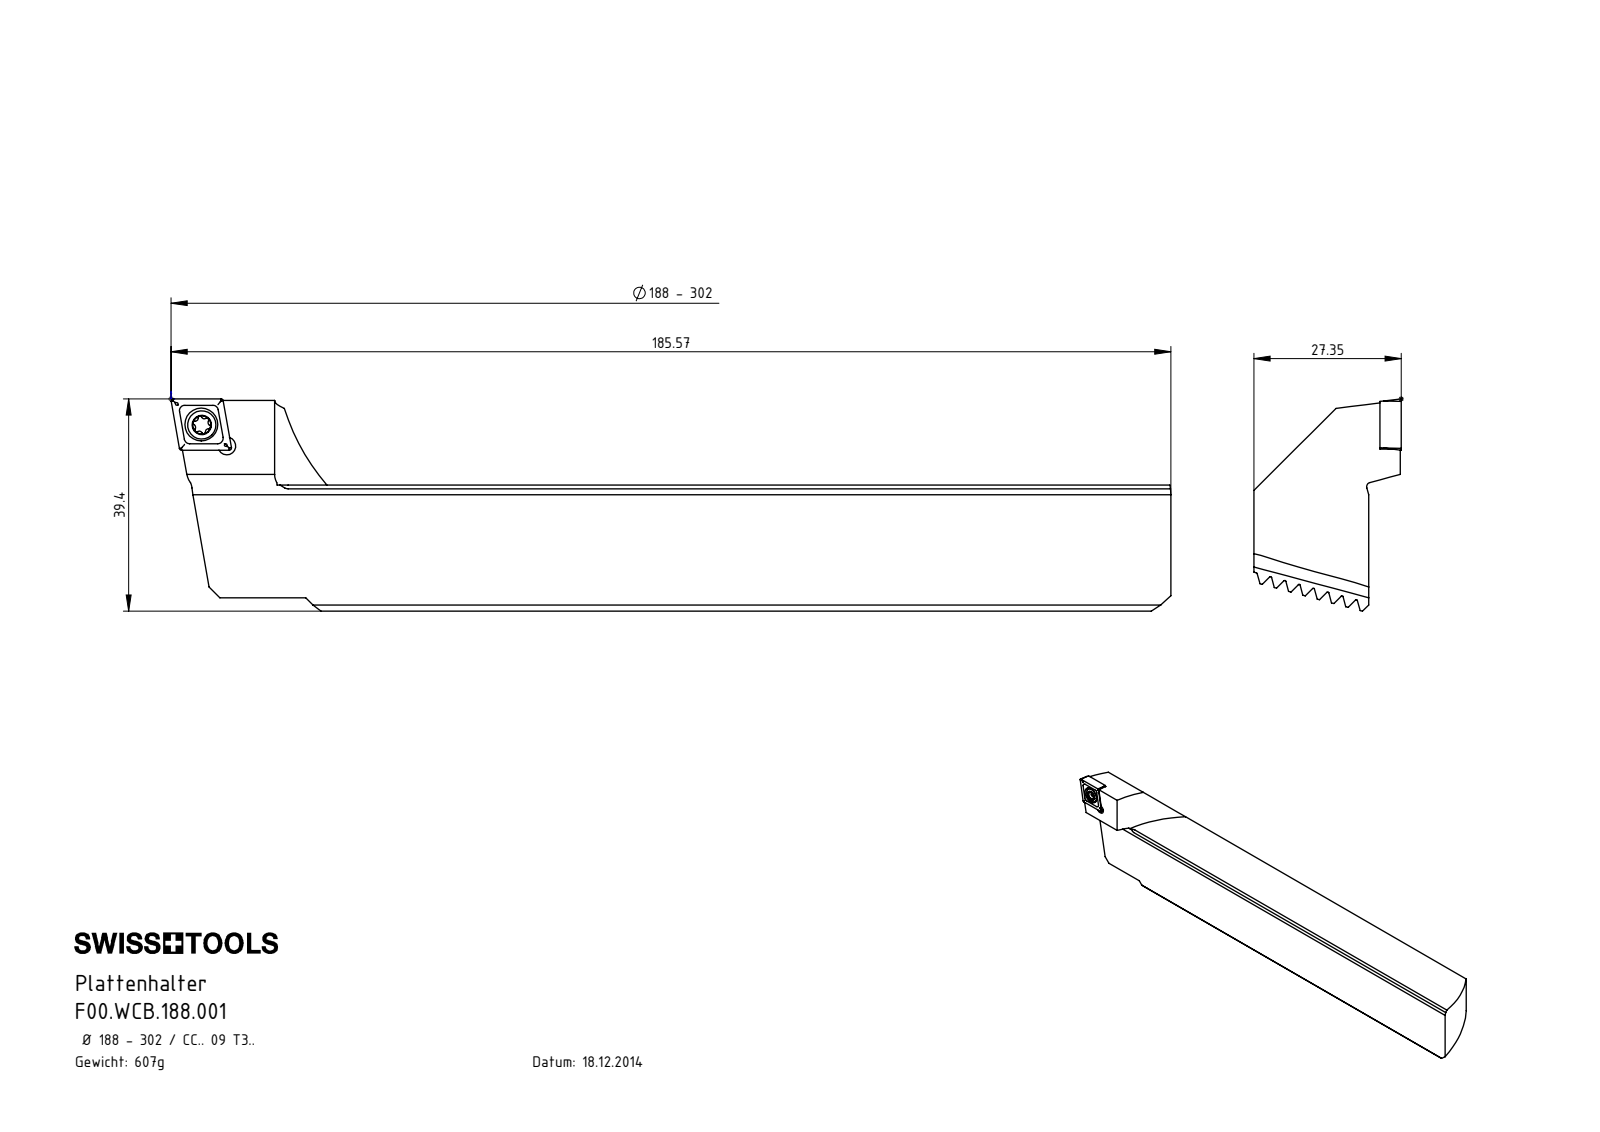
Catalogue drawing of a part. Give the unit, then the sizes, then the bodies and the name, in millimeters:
Units: millimetres
Overall size (bounding box): 185.57 × 39.4 × 27.35
Round holes (diameter × count): ⌀3.3 ×2, ⌀4.4 ×1, ⌀6.1 ×1
Round bosses / shafts (diameter × count): ⌀5.25 ×1, ⌀4 ×1
Partial cylindrical surfaces — rounded edges, fillets, slot ends (radius × count): R0.2 ×8, R0.34 ×6, R0.59 ×6, R40 ×3, R0.8 ×1
Main face-to-face distances: 2.38, 21.3, 4.76, 7.14, 9.52, 4.77, 7.15, 9.53, 11.91, 14.29
Hole centre spacings: 6.06, 6.19
Volume: 77 331 mm³ · Surface area: 18 926 mm²
Bodies: 3 solids, 694 faces (422 planar, 39 cylindrical, 233 other)
Part name (STEP PRODUCT): CCMT09T304; F00.WCB.188.001; WCB-ER2.001.009_A; F00-WCB.188.001_C
STEP written by: SolidWorks 2017 (AUTOMOTIVE_DESIGN)
